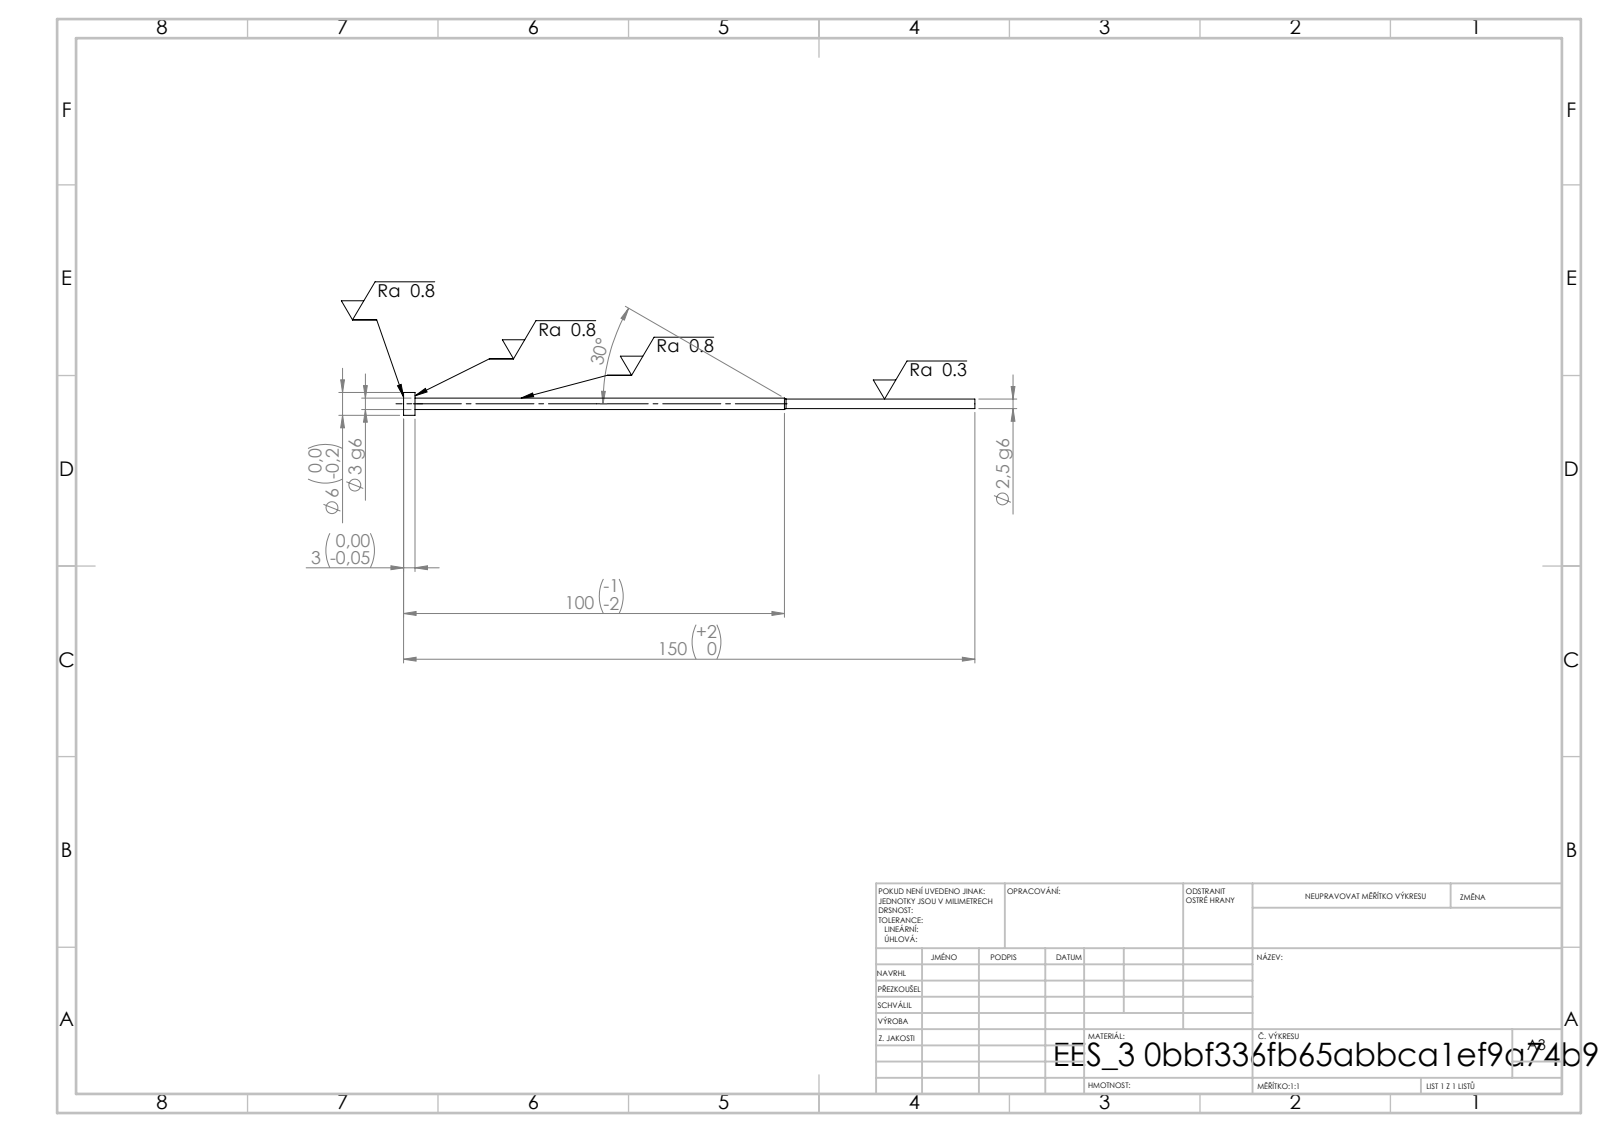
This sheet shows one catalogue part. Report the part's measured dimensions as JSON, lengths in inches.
{"step_written_by": "SolidWorks 2019 (CONFIG_CONTROL_DESIGN)", "units": "inches", "bodies": {"solids": 1, "faces": 11, "planar": 3, "cylindrical": 6, "other": 2}, "overall_size": [5.906, 0.236, 0.236], "volume_in3": 0.062, "surface_area_in2": 2.199, "round_bosses_or_shafts": [[0.236, 1], [0.118, 1], [0.098, 1]], "face_to_face_distances": [0.118, 5.787, 5.906]}
